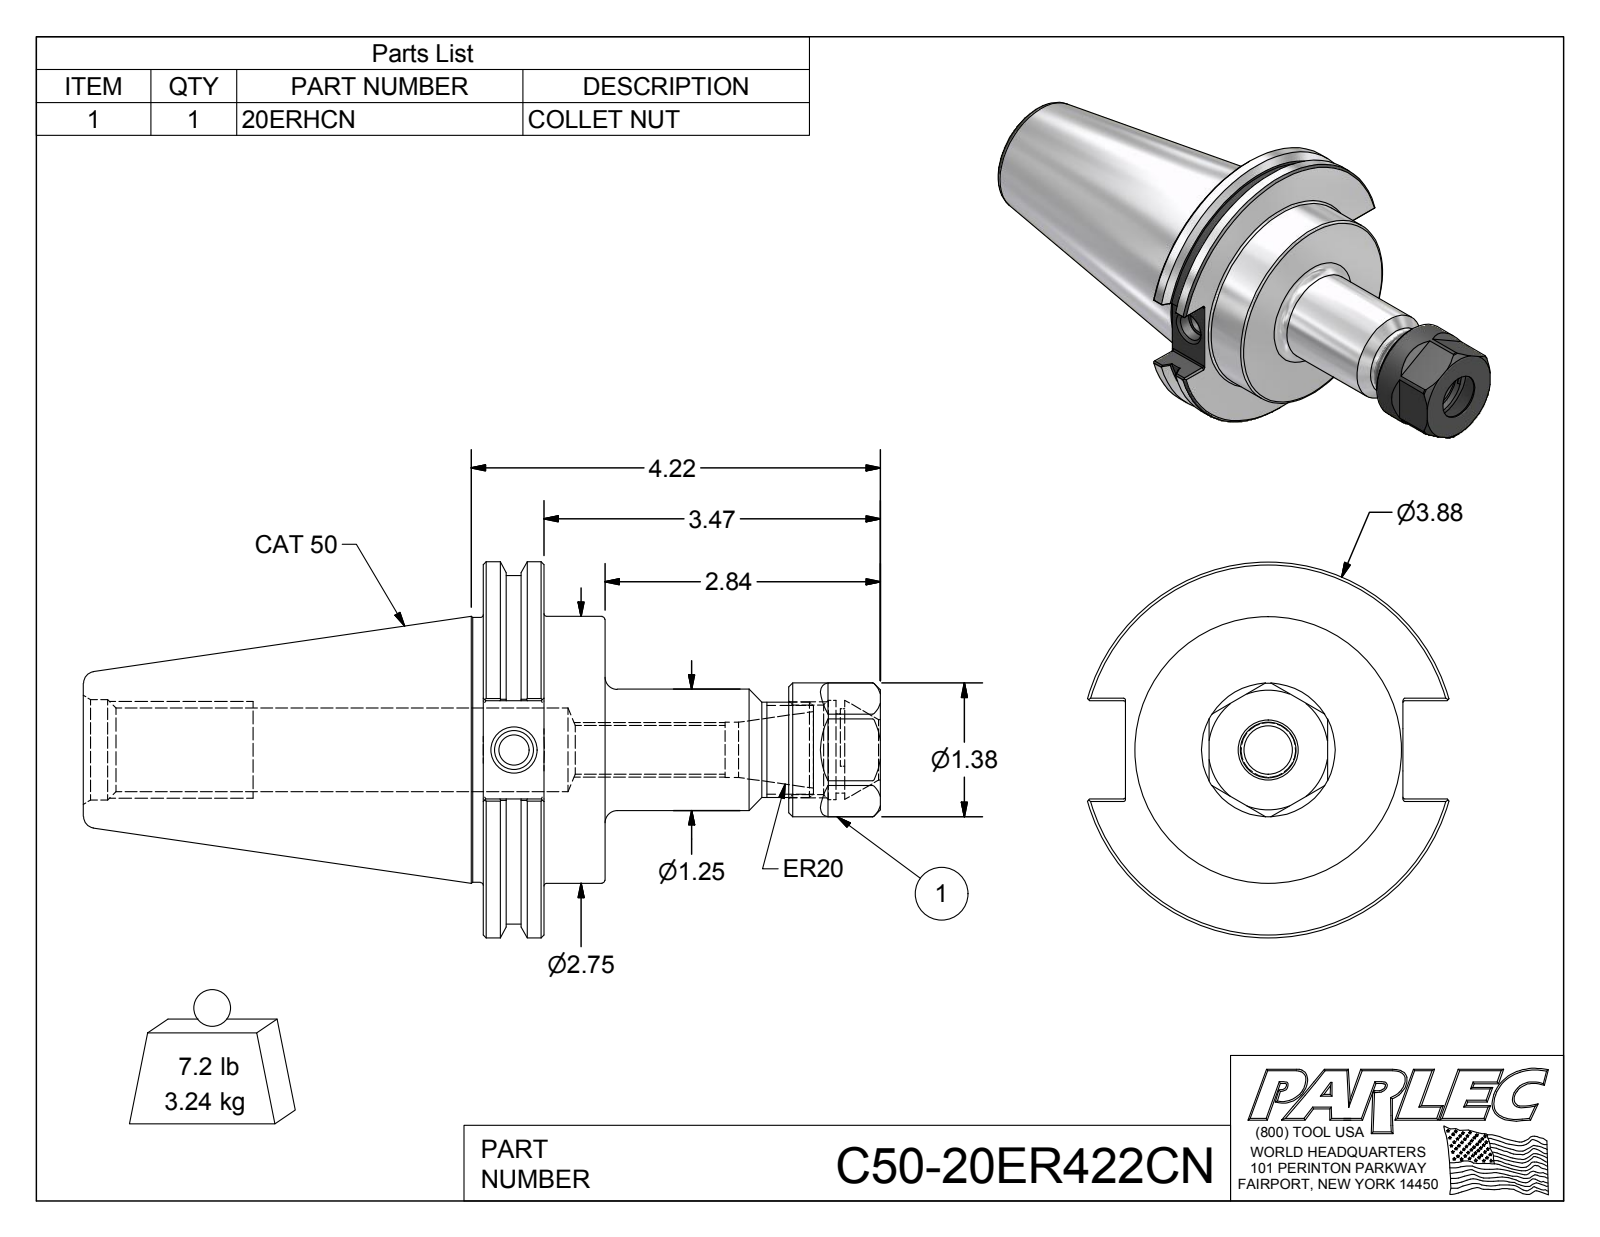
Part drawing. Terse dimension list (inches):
name: C50-20ER422CN; C50-20ER4-1; 20ERHCN
written by: Autodesk Inventor 2012 (AUTOMOTIVE_DESIGN)
unit: in
bodies: 2 solids, 132 faces (50 planar, 34 cylindrical, 48 other)
size: 8.22 × 3.875 × 3.729
volume: 25.38 in³; area: 95.33 in²
holes: 1× ⌀0.315, 1× ⌀0.399, 1× ⌀0.502, 1× ⌀0.57, 1× ⌀0.62, 1× ⌀0.82, 1× ⌀0.865, 1× ⌀0.925, 1× ⌀1.024, 1× ⌀1.038
bosses: 1× ⌀3.875, 1× ⌀3.594, 1× ⌀2.75, 1× ⌀2.73, 1× ⌀1.378, 1× ⌀1.25, 1× ⌀0.984
rounds: 12× R0.02, 1× R0.423
face distances: 0.625, 1.255, 0.63, 1.22, 4.095, 3.47, 2.84, 3.15, 2.525, 1.895
hole spacings: 0.037
